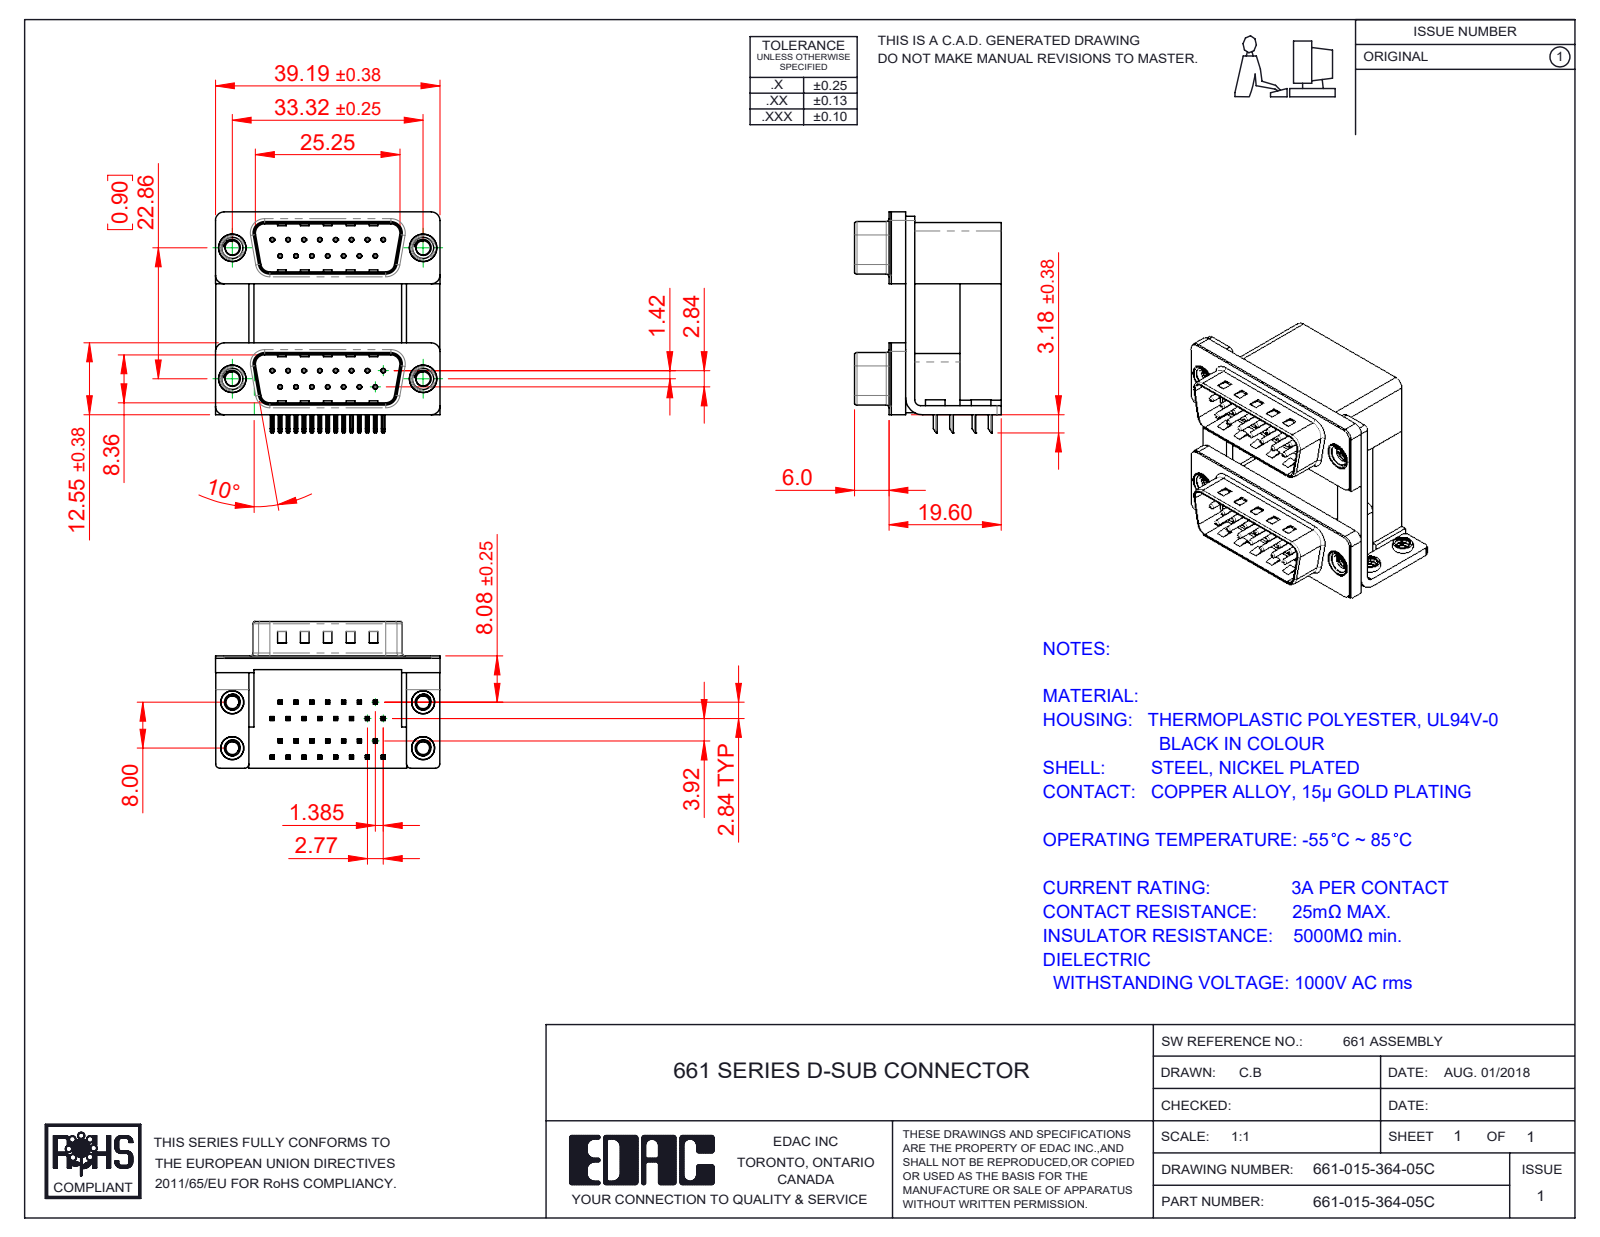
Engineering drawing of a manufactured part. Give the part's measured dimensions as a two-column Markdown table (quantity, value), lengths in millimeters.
| quantity | value |
| --- | --- |
| part name | 661-015-364-05C; 661 Contact Top Upper_H; 661 Shell_15 Contacts; 661 Housing Spacer_15 Contacts H (+8 more) |
| STEP written by | SolidWorks 2020 (CONFIG_CONTROL_DESIGN) |
| units | millimeters |
| bodies | 45 solids, 3106 faces (1846 planar, 938 cylindrical, 322 other) |
| overall size | 39.19 × 38.59 × 25.6 |
| volume | 15 182 mm³ |
| surface area | 16 626 mm² |
| round holes (diameter × count) | 0.35 × 30, 0.8 × 30, 2.26 × 4, 2.5 × 4, 2.75 × 4, 3.2 × 4, 3.5 × 4, 4 × 4, 4.8 × 4, 5 × 4 |
| round bosses / shafts (diameter × count) | 0.75 × 30, 4.9 × 4, 4.75 × 4, 4 × 4, 3.9 × 4, 3.4 × 4 |
| partial cylindrical surfaces (radius × count) | 0.25 × 120, 0.12 × 60, 0.5 × 16, 1.5 × 15, 0.75 × 8, 0.9 × 8, 1.6 × 8, 2 × 8 |
| main face-to-face distances | 0.4, 22.86, 12, 19.2, 7.2, 16.7, 9.5, 2.5, 12.4, 10.7 |
| hole center spacings | 3.16, 2.77, 23.03, 5.54, 23.52, 8.31, 22.86, 24.32 |
